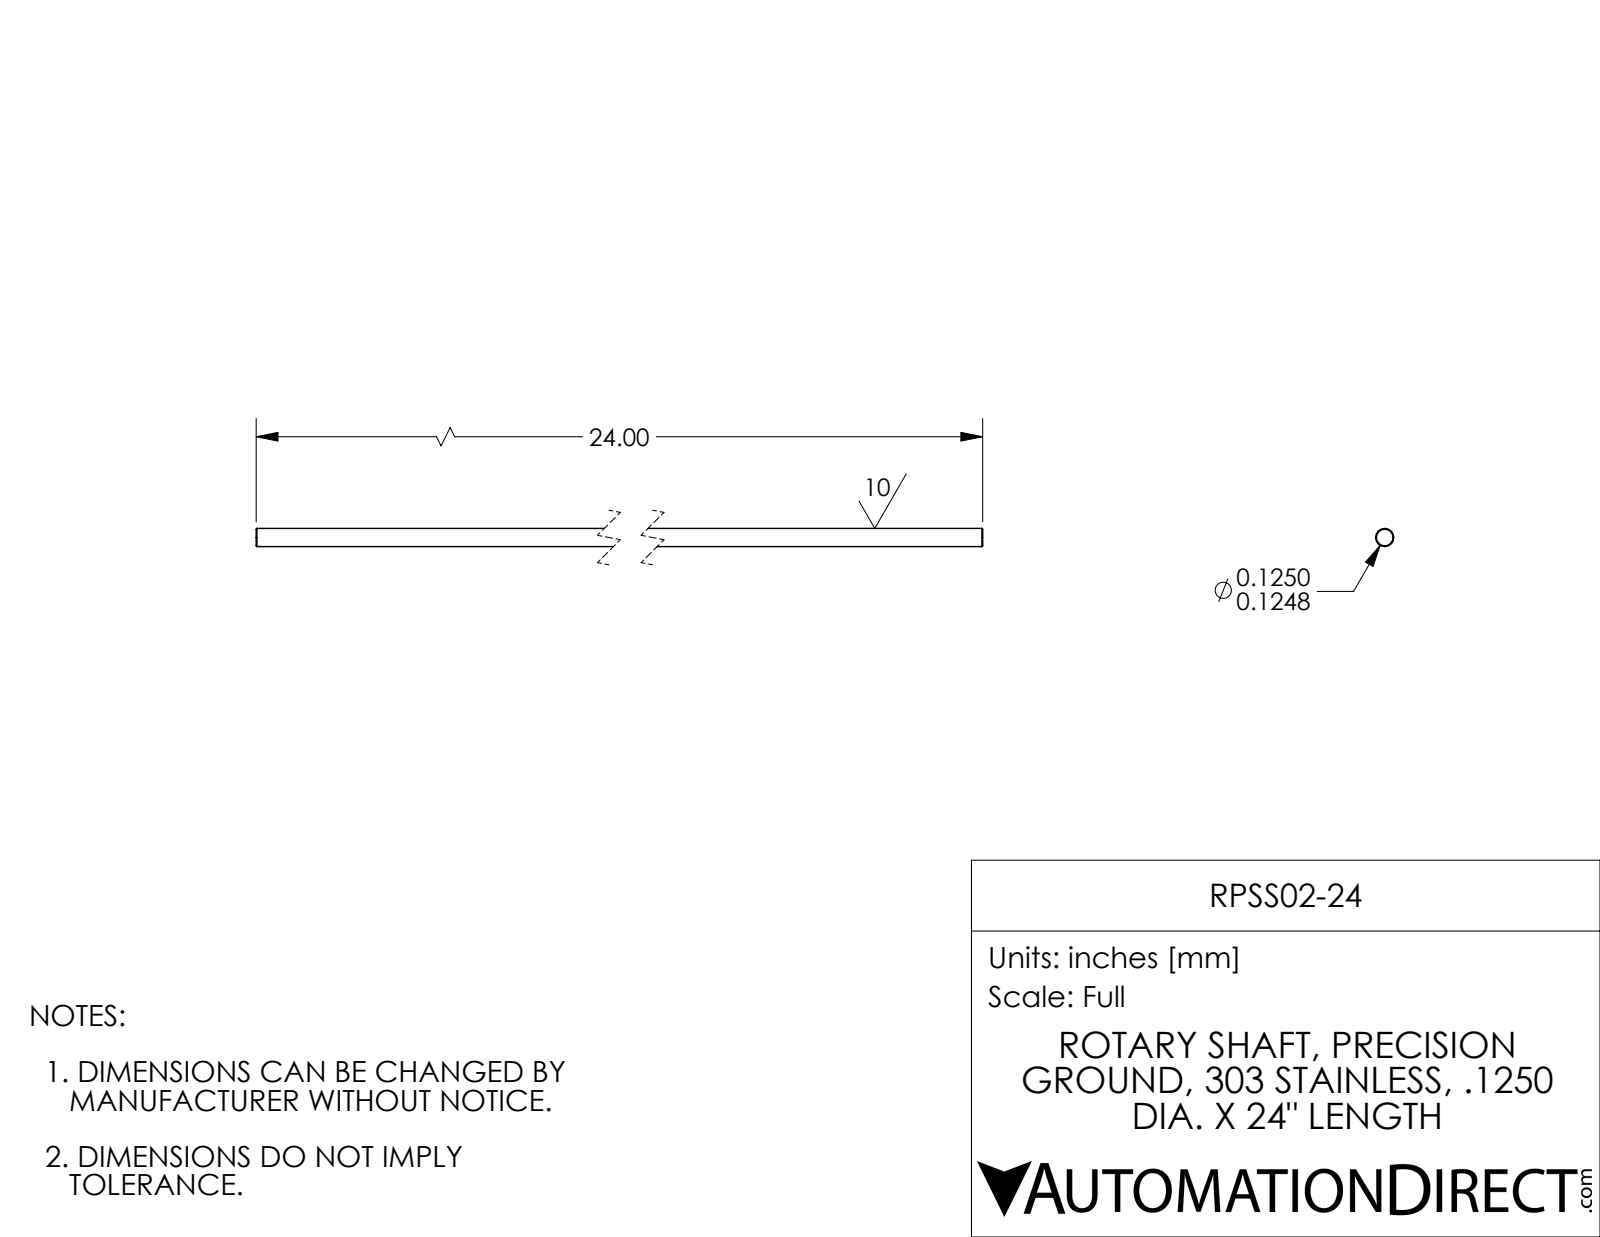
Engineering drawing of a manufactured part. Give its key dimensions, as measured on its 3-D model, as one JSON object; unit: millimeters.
{"part_name": "RPSS02-24", "step_written_by": "SolidWorks 2017 (AUTOMOTIVE_DESIGN)", "units": "millimeters", "bodies": {"solids": 1, "faces": 8, "planar": 2, "cylindrical": 2, "other": 4}, "overall_size": [609.6, 3.2, 3.2], "volume_mm3": 4830, "surface_area_mm2": 6095, "round_bosses_or_shafts": [[3.2, 1]], "face_to_face_distances": [609.6]}
